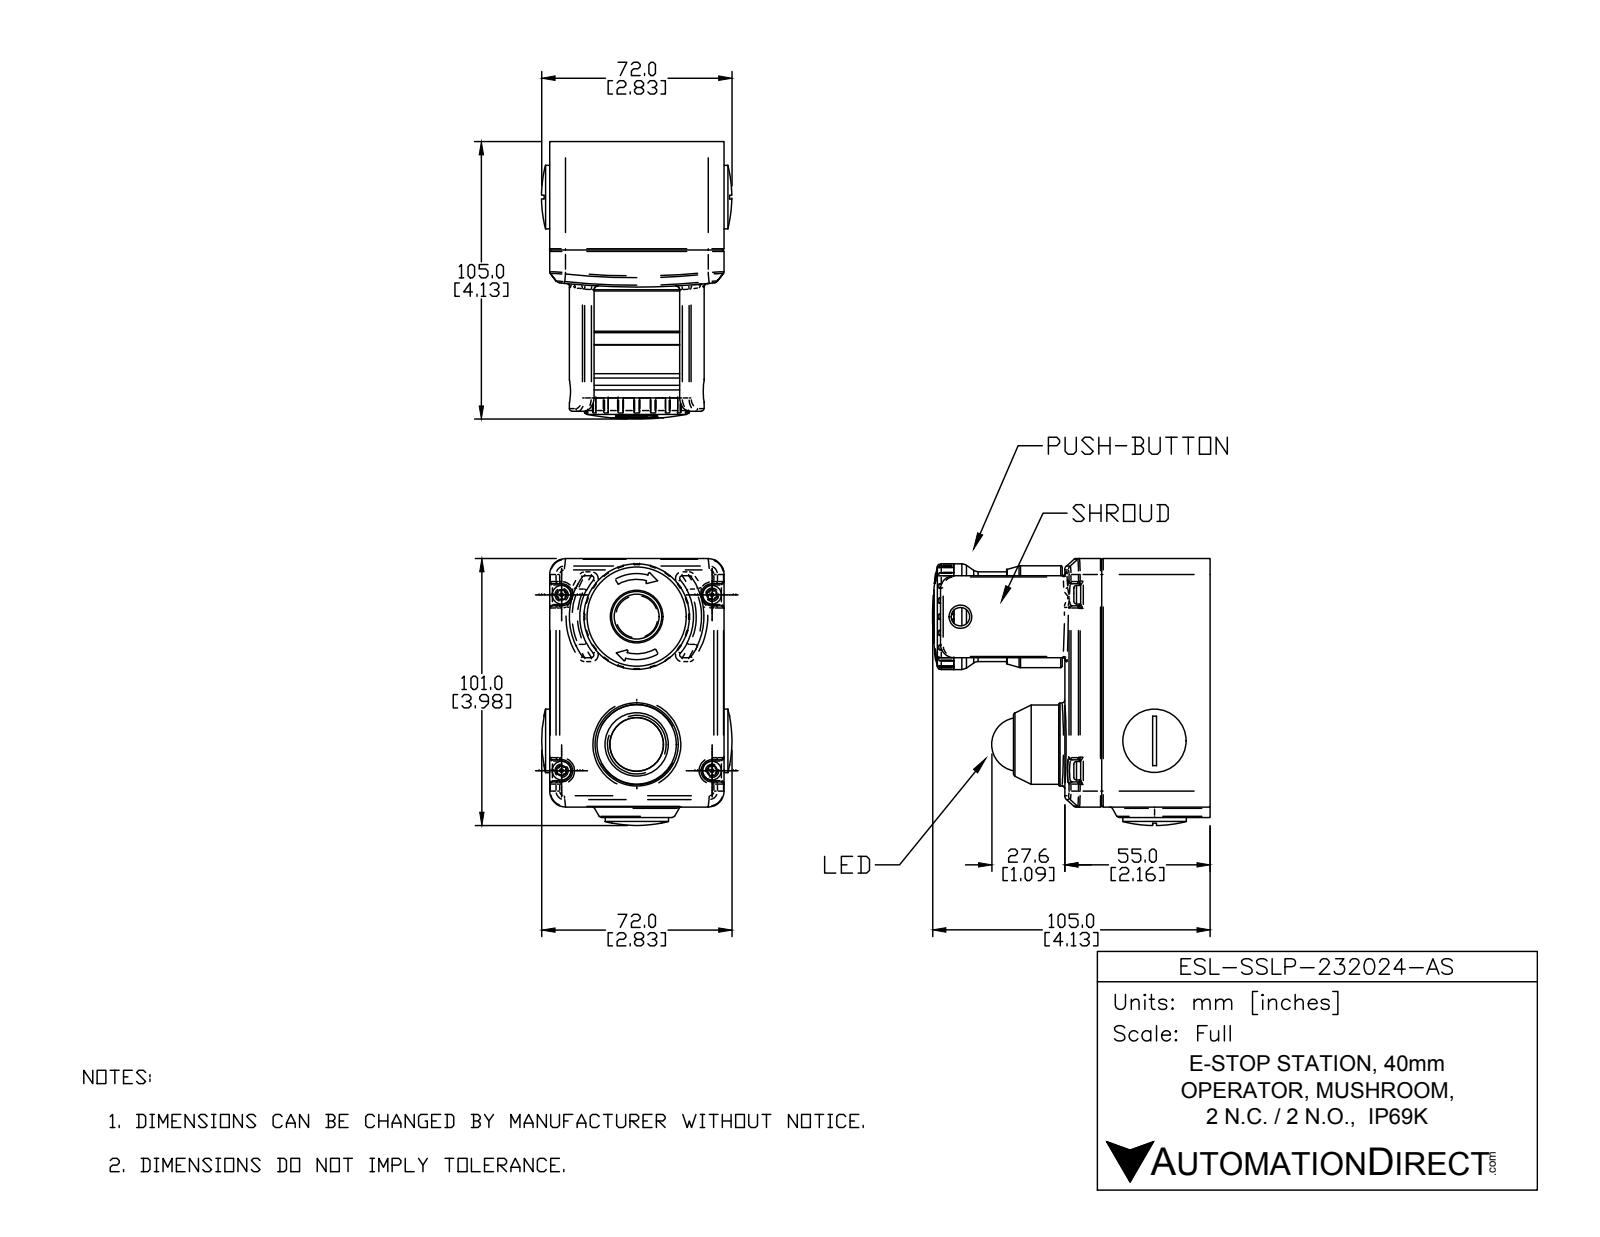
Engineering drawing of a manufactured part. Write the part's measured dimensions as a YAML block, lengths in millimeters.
part_name: "ESL-SSLP-232024-AS"
step_written_by: "SolidWorks 2016 (AUTOMOTIVE_DESIGN)"
units: millimeters
bodies: {solids: 13, faces: 797, planar: 227, cylindrical: 287, other: 283}
overall_size: [105, 100.99, 71.98]
volume: 382565
surface_area: 72756
round_holes:
  - {diameter: 4.5, count: 4}
  - {diameter: 7, count: 1}
  - {diameter: 28.04, count: 1}
  - {diameter: 31.1, count: 1}
  - {diameter: 37, count: 1}
round_bosses_or_shafts:
  - {diameter: 7, count: 4}
  - {diameter: 1, count: 4}
  - {diameter: 24, count: 2}
  - {diameter: 40, count: 1}
  - {diameter: 38.6, count: 1}
  - {diameter: 34, count: 1}
  - {diameter: 31.4, count: 1}
  - {diameter: 30, count: 1}
partial_cylinders:
  - {radius: 0.1, count: 80}
  - {radius: 0.76, count: 24}
  - {radius: 0.5, count: 14}
  - {radius: 1, count: 13}
  - {radius: 1.5, count: 6}
  - {radius: 0.2, count: 4}
  - {radius: 4.2, count: 4}
  - {radius: 6, count: 4}
face_to_face_distances: [41, 66, 56, 15, 98, 4, 94, 56.8, 15.8, 0.8]
hole_center_spacings: [31.38, 32.23, 54, 69.83, 71.31, 82, 98.18, 48.4]
